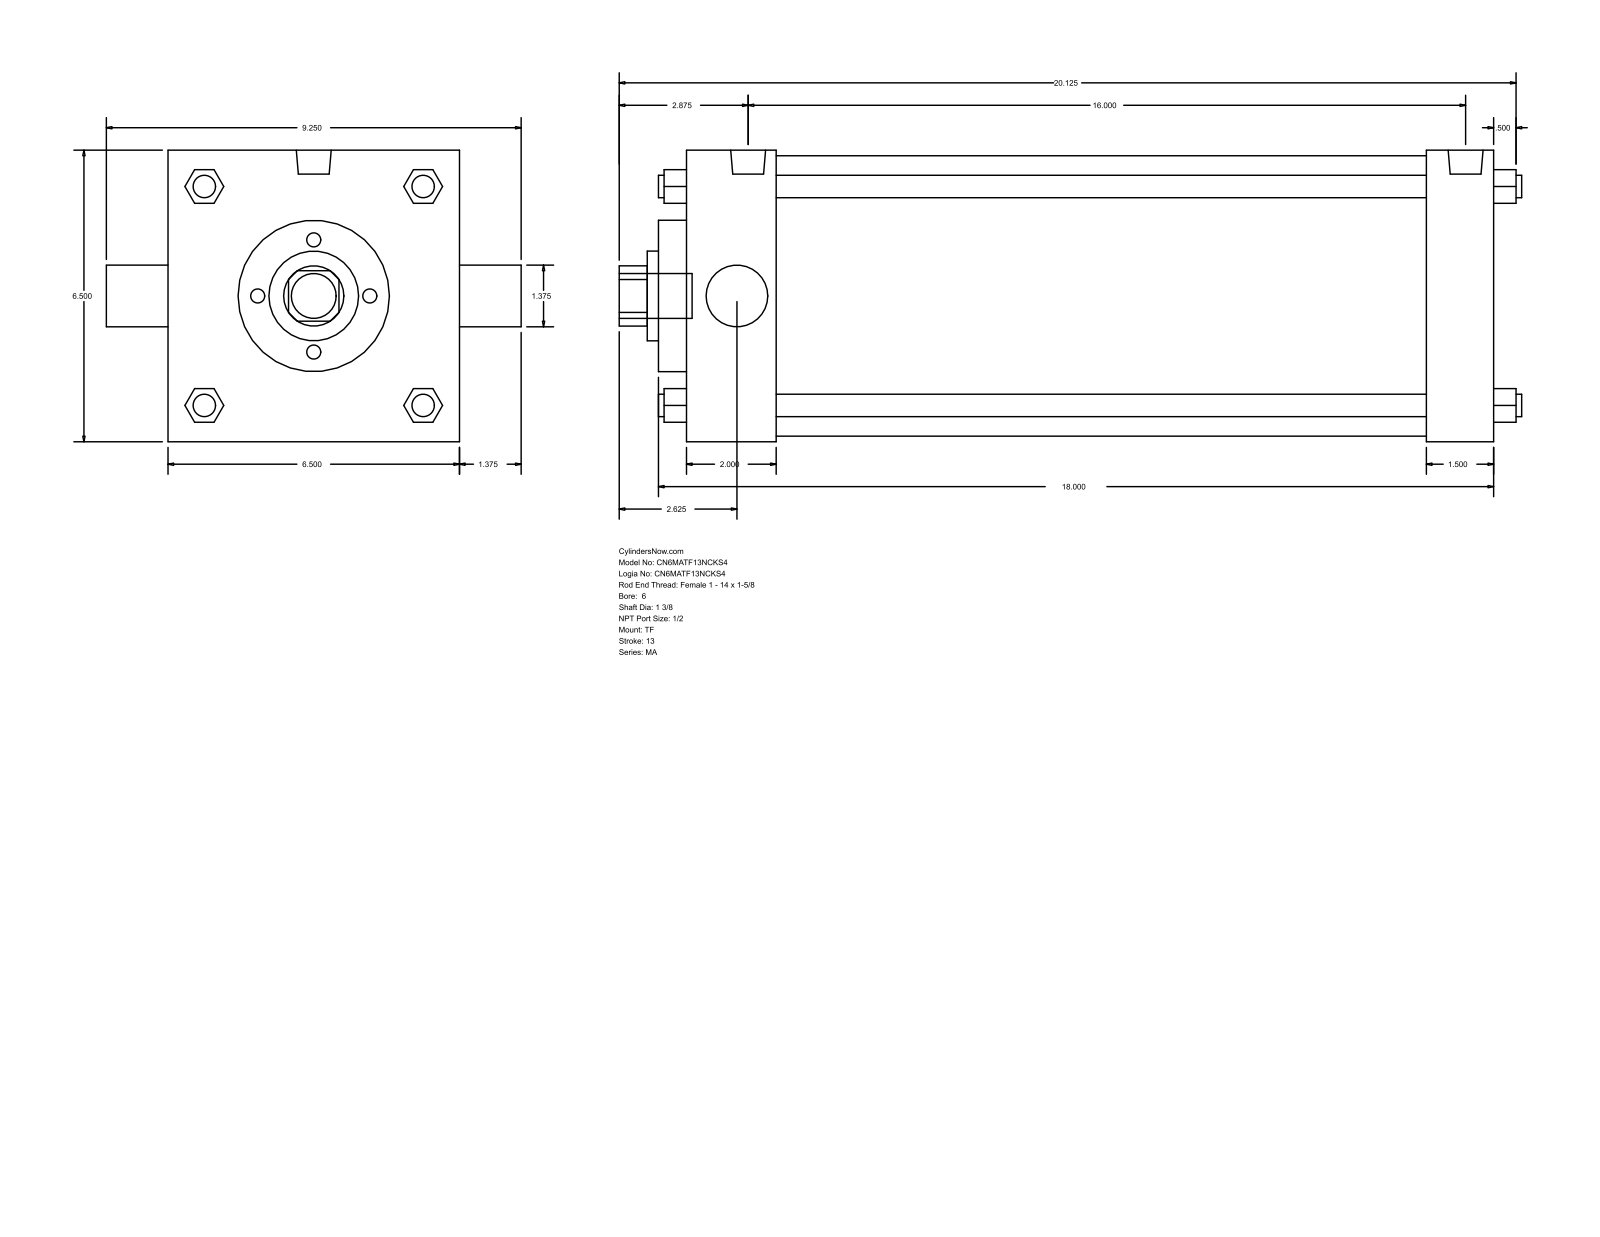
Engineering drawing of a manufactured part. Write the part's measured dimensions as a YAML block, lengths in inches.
part_name: "MA_TF__0600_1.375"
step_written_by: "GSSL Pune (CONFIG_CONTROL_DESIGN)"
units: inches
bodies: {solids: 0, faces: 122, planar: 93, cylindrical: 29, other: 0}
overall_size: [20.125, 9.25, 6.5]
round_holes:
  - {diameter: 1.375, count: 2}
  - {diameter: 2, count: 1}
  - {diameter: 3.375, count: 1}
  - {diameter: 6.25, count: 1}
round_bosses_or_shafts:
  - {diameter: 0.5, count: 4}
  - {diameter: 0.687, count: 3}
  - {diameter: 0.778, count: 2}
  - {diameter: 1, count: 1}
partial_cylinders:
  - {radius: 0.672, count: 1}
face_to_face_distances: [6.5, 18.125, 2, 16.625, 1.5, 16.125, 14.625, 0.625, 2.625, 17.25]
